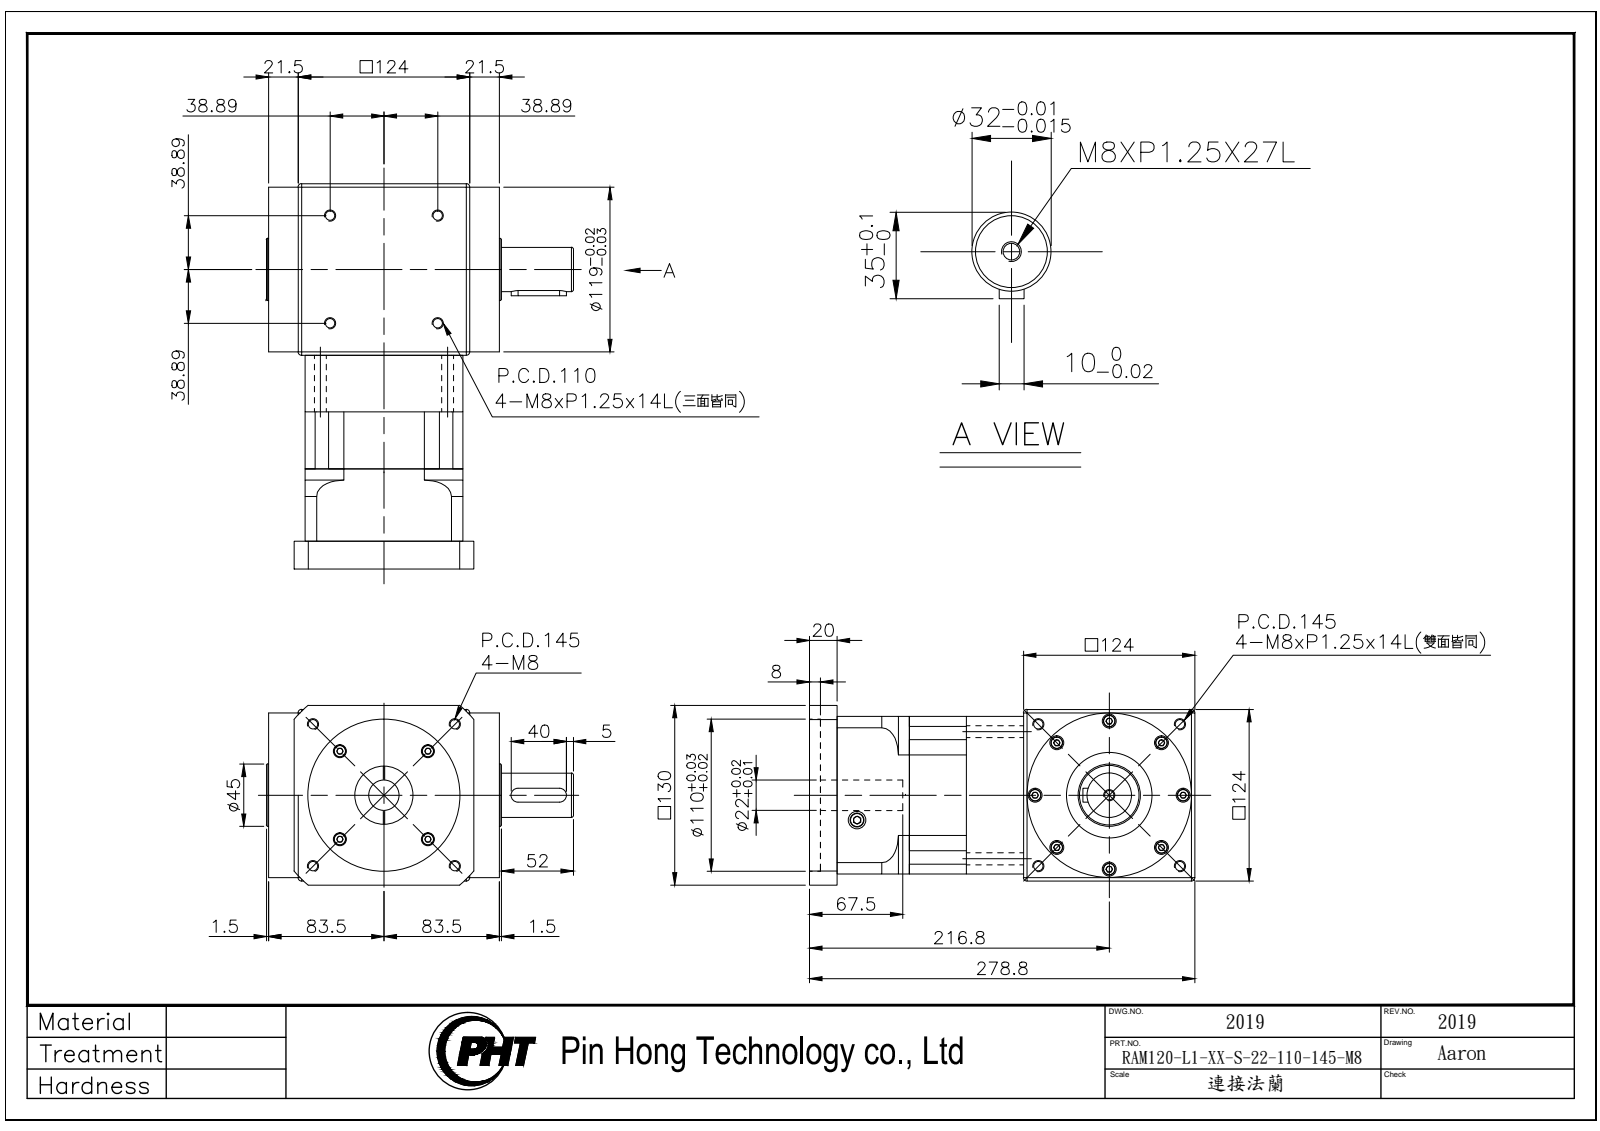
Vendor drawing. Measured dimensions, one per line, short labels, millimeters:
name: RAM120-L1-XX-S-22-110-145-M8_2019
written by: SolidWorks 2016 (AUTOMOTIVE_DESIGN)
unit: mm
bodies: 5 solids, 977 faces (484 planar, 317 cylindrical, 176 other)
size: 278.8 × 222 × 130
volume: 4 215 000 mm³; area: 347 446 mm²
holes: 17× ⌀6.8, 12× ⌀9.5, 8× ⌀5.3, 8× ⌀9, 8× ⌀14, 4× ⌀4.2, 4× ⌀5.5, 4× ⌀8.6, 2× ⌀12.7, 1× ⌀4.08, 1× ⌀22, 1× ⌀42
bosses: 12× ⌀13, 12× ⌀8.5, 1× ⌀119, 1× ⌀62, 1× ⌀49, 1× ⌀45, 1× ⌀32
rounds: 4× R7, 2× R5, 1× R64, 1× R75, 1× R85, 1× R86.2
face distances: 124, 5, 119, 41.5, 114, 3, 41, 82.5, 8, 206.5
hole spacings: 59, 10, 15.4, 17.24, 19.42, 21.77, 39.8, 51.28
